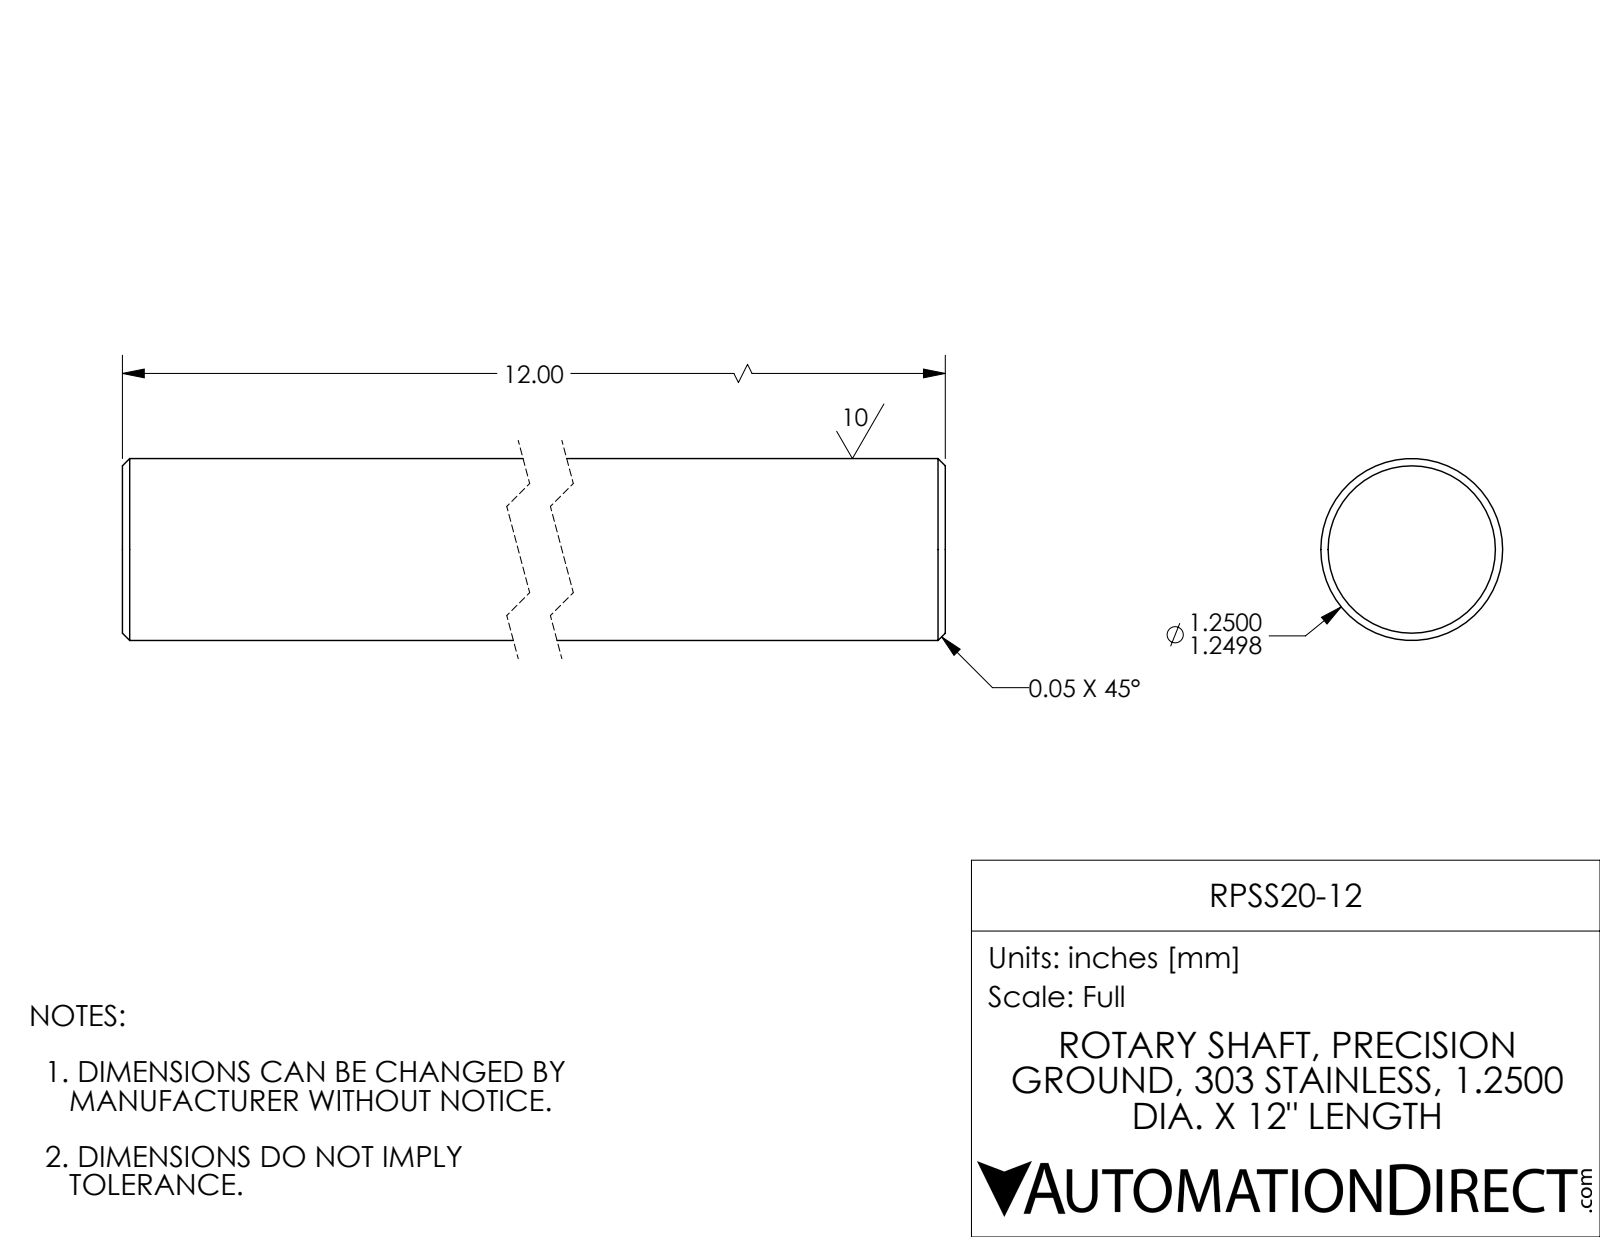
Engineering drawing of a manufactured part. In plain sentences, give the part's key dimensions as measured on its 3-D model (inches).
The part is named "RPSS20-12". Its 3-D file was written by "SolidWorks 2017 (AUTOMOTIVE_DESIGN)". It is 1 solid with 8 faces: 2 planar, 2 cylindrical and 4 other. Overall it measures 12 by 1.25 by 1.25 inches. Its volume is 14.72 cubic inches and its surface area 49.34 square inches. Round bosses or shafts: 1 of diameter 1.25. The main face-to-face distances are 12.
